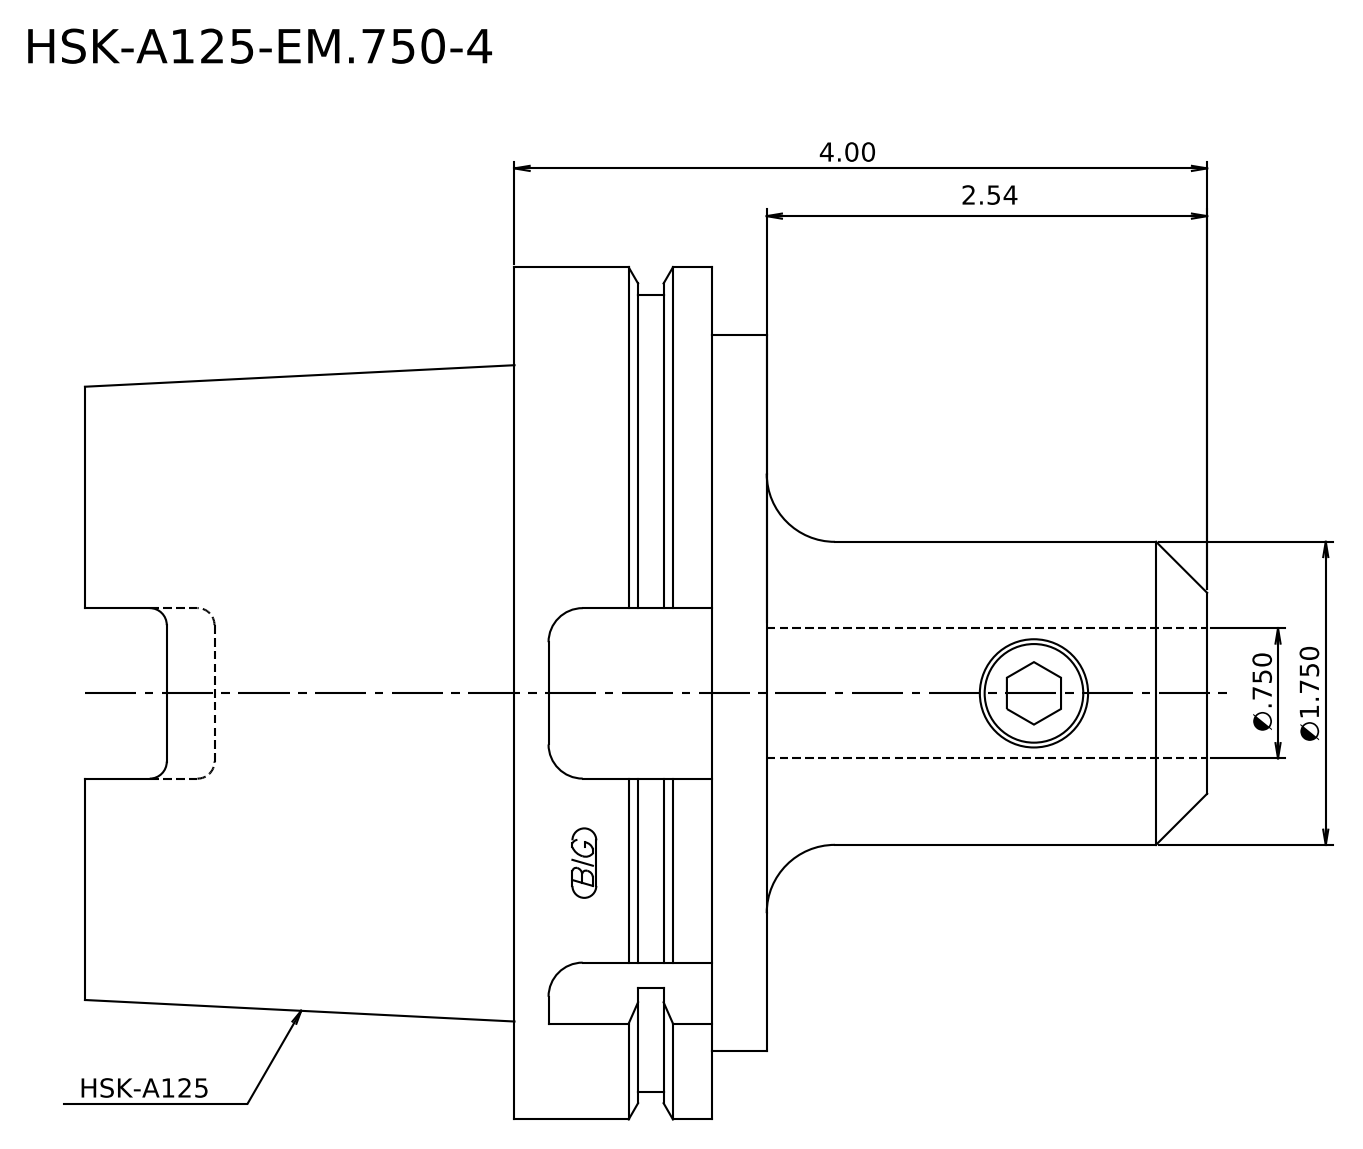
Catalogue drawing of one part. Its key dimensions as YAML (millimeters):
step_written_by: "Kubotek KeyCreator 2011 V10.0.2 (22737) (automotive_design)"
units: millimeters
bodies: {solids: 1, faces: 17, planar: 7, cylindrical: 5, other: 5}
overall_size: [164.6, 125, 125]
volume: 952150
surface_area: 65901
round_bosses_or_shafts:
  - {diameter: 125, count: 1}
  - {diameter: 117, count: 1}
  - {diameter: 105, count: 1}
  - {diameter: 44.45, count: 1}
face_to_face_distances: [100, 37, 63, 8, 29, 92, 64.6, 72.6, 101.6, 164.6]
